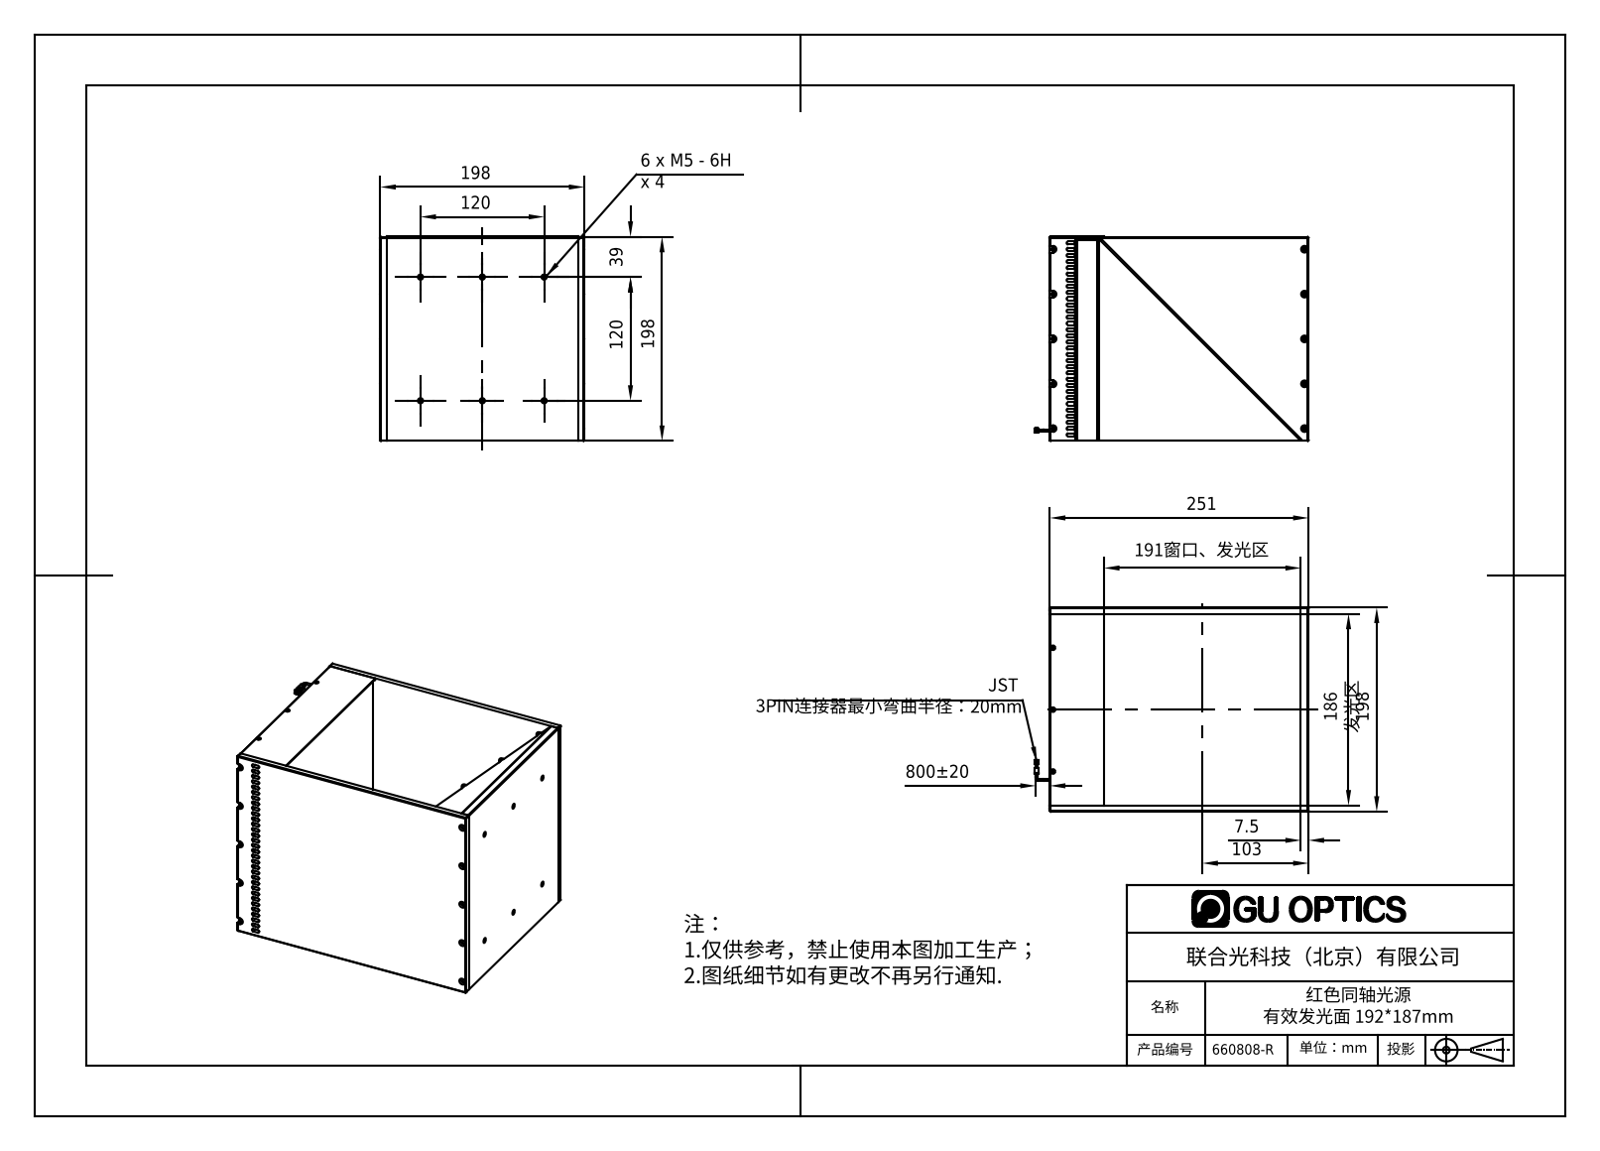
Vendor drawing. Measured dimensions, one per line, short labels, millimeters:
name: 红色同轴光源 有效发光面 192187mm
written by: SolidWorks 2016 (AUTOMOTIVE_DESIGN)
unit: mm
bodies: 21 solids, 4677 faces (3722 planar, 818 cylindrical, 137 other)
size: 266 × 198.2 × 198
volume: 1 344 000 mm³; area: 786 582 mm²
holes: 26× ⌀2.5, 10× ⌀3, 10× ⌀3.4, 6× ⌀4.2, 6× ⌀5, 5× ⌀6.5, 5× ⌀7, 4× ⌀38, 4× ⌀48, 4× ⌀58, 3× ⌀1.6, 3× ⌀2
bosses: 4× ⌀51, 4× ⌀41, 2× ⌀1.75
rounds: 64× R1.5, 32× R1.76, 32× R1.76, 32× R1.77, 9× R1.1, 8× R0.5, 8× R0.9, 8× R1.05
face distances: 198, 192, 6, 2, 1.5, 196, 186, 205.5, 1.6, 203.5
hole spacings: 50, 35.36, 244, 70.71, 102.96, 87, 90, 100
